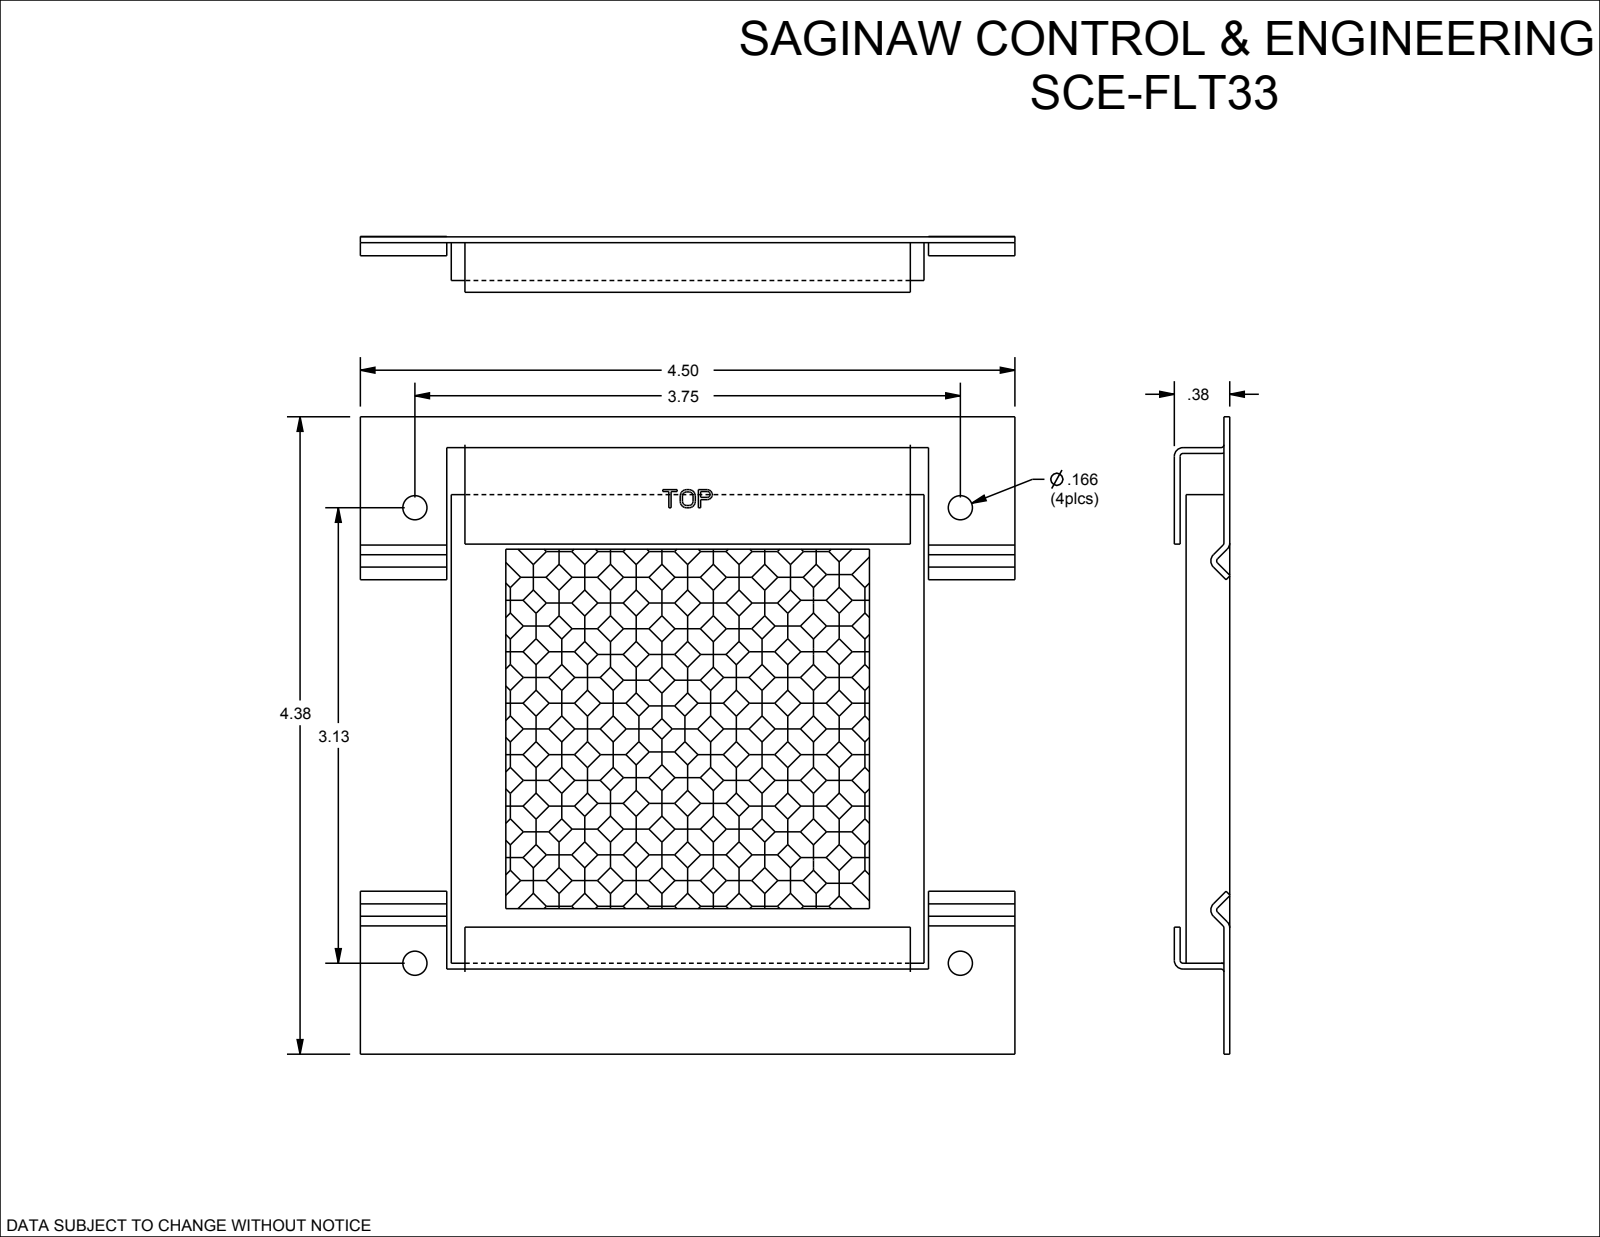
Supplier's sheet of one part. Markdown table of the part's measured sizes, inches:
| quantity | value |
| --- | --- |
| part name | SCE-FLT33 |
| STEP written by | SolidWorks 2019 (CONFIG_CONTROL_DESIGN) |
| units | inches |
| bodies | 3 solids, 810 faces (294 planar, 516 cylindrical, 0 other) |
| overall size | 4.5 × 4.38 × 0.384 |
| volume | 2.202 in³ |
| surface area | 51.67 in² |
| round holes (diameter × count) | 0.166 × 4 |
| round bosses / shafts (diameter × count) | 0.125 × 18, 0.125 × 8 |
| partial cylindrical surfaces (radius × count) | 0.02 × 8, 0.06 × 8 |
| main face-to-face distances | 0.04, 0.26, 0.3, 0.04, 0.081, 0.341, 0.381, 0.041, 0.301, 0.341 |
| hole center spacings | 3.13, 3.75, 4.885 |
